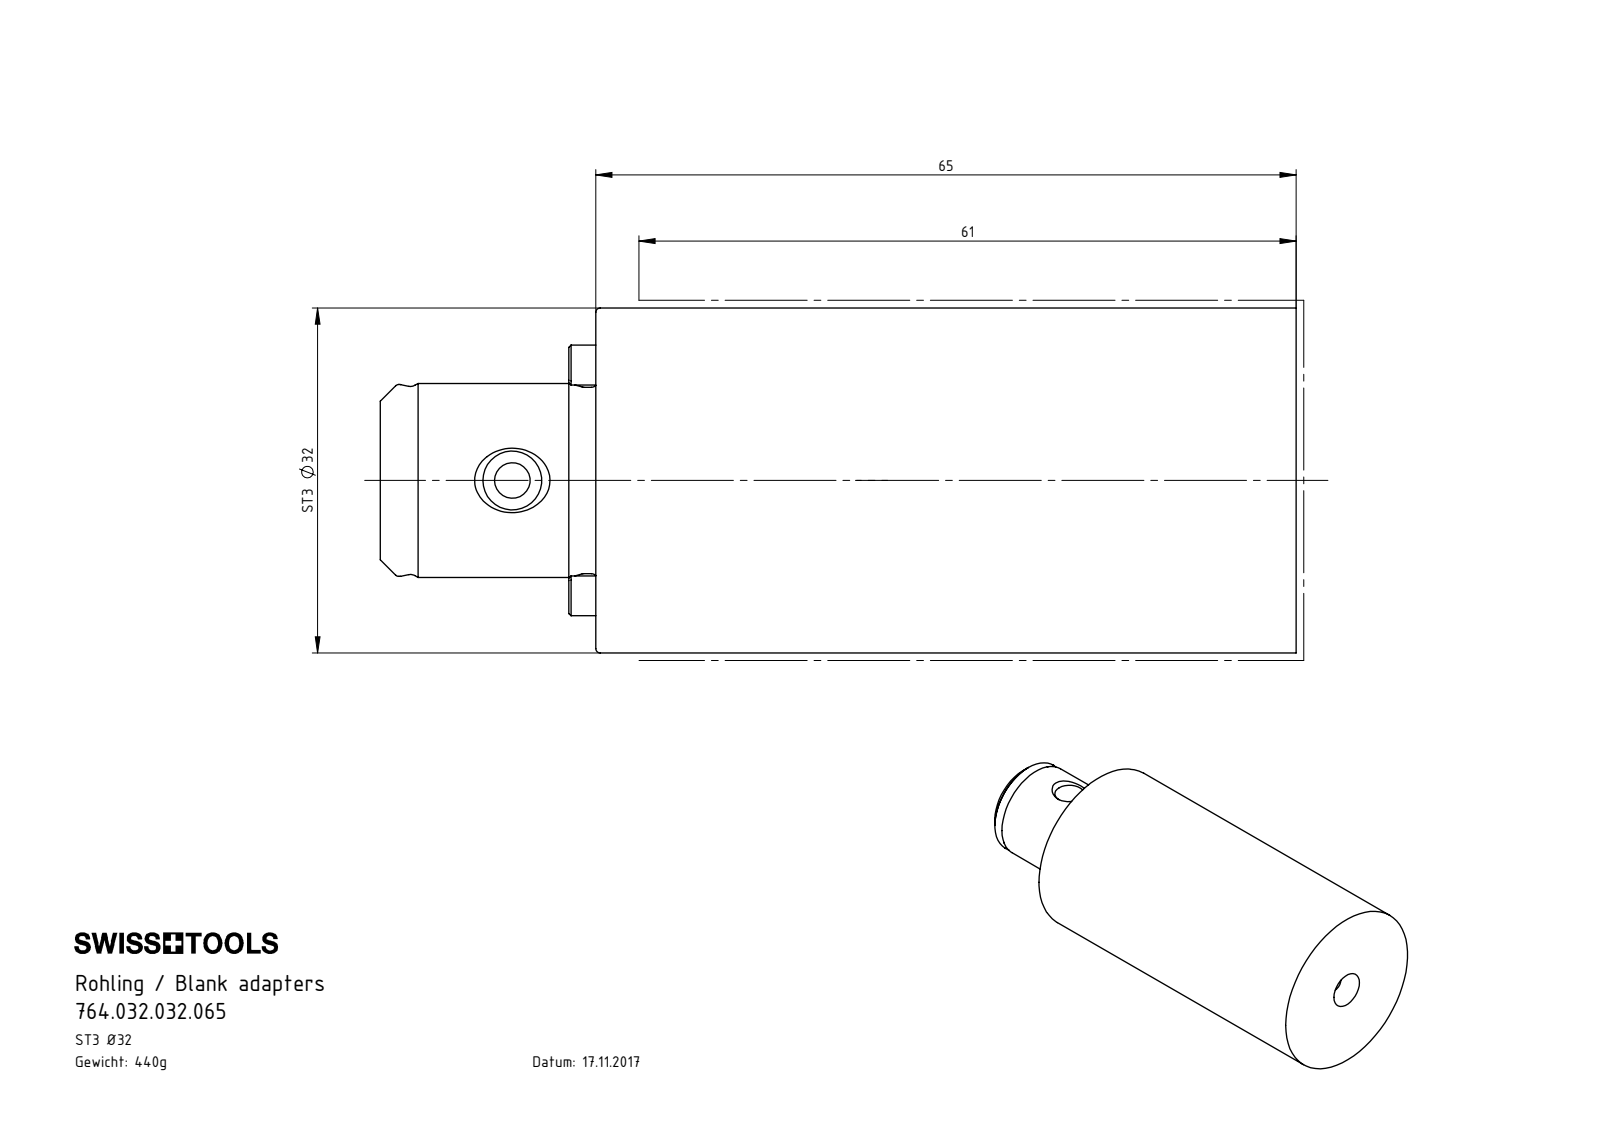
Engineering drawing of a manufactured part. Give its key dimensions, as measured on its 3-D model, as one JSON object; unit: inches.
{"part_name": "ST3-Ro1.001.065_B; ST3-Ro1.001.065", "step_written_by": "SolidWorks 2015 (CONFIG_CONTROL_DESIGN)", "units": "inches", "bodies": {"solids": 1, "faces": 69, "planar": 3, "cylindrical": 20, "other": 46}, "overall_size": [3.346, 1.26, 1.26], "volume_in3": 3.413, "surface_area_in2": 15.44, "round_holes": [[0.11, 2], [0.124, 1], [0.13, 1], [0.268, 1], [0.354, 1]], "round_bosses_or_shafts": [[1.26, 1], [0.709, 1], [0.701, 1], [0.681, 1]], "face_to_face_distances": [2.559, 0.787, 3.346], "hole_center_spacings": [0.427, 0.854]}
